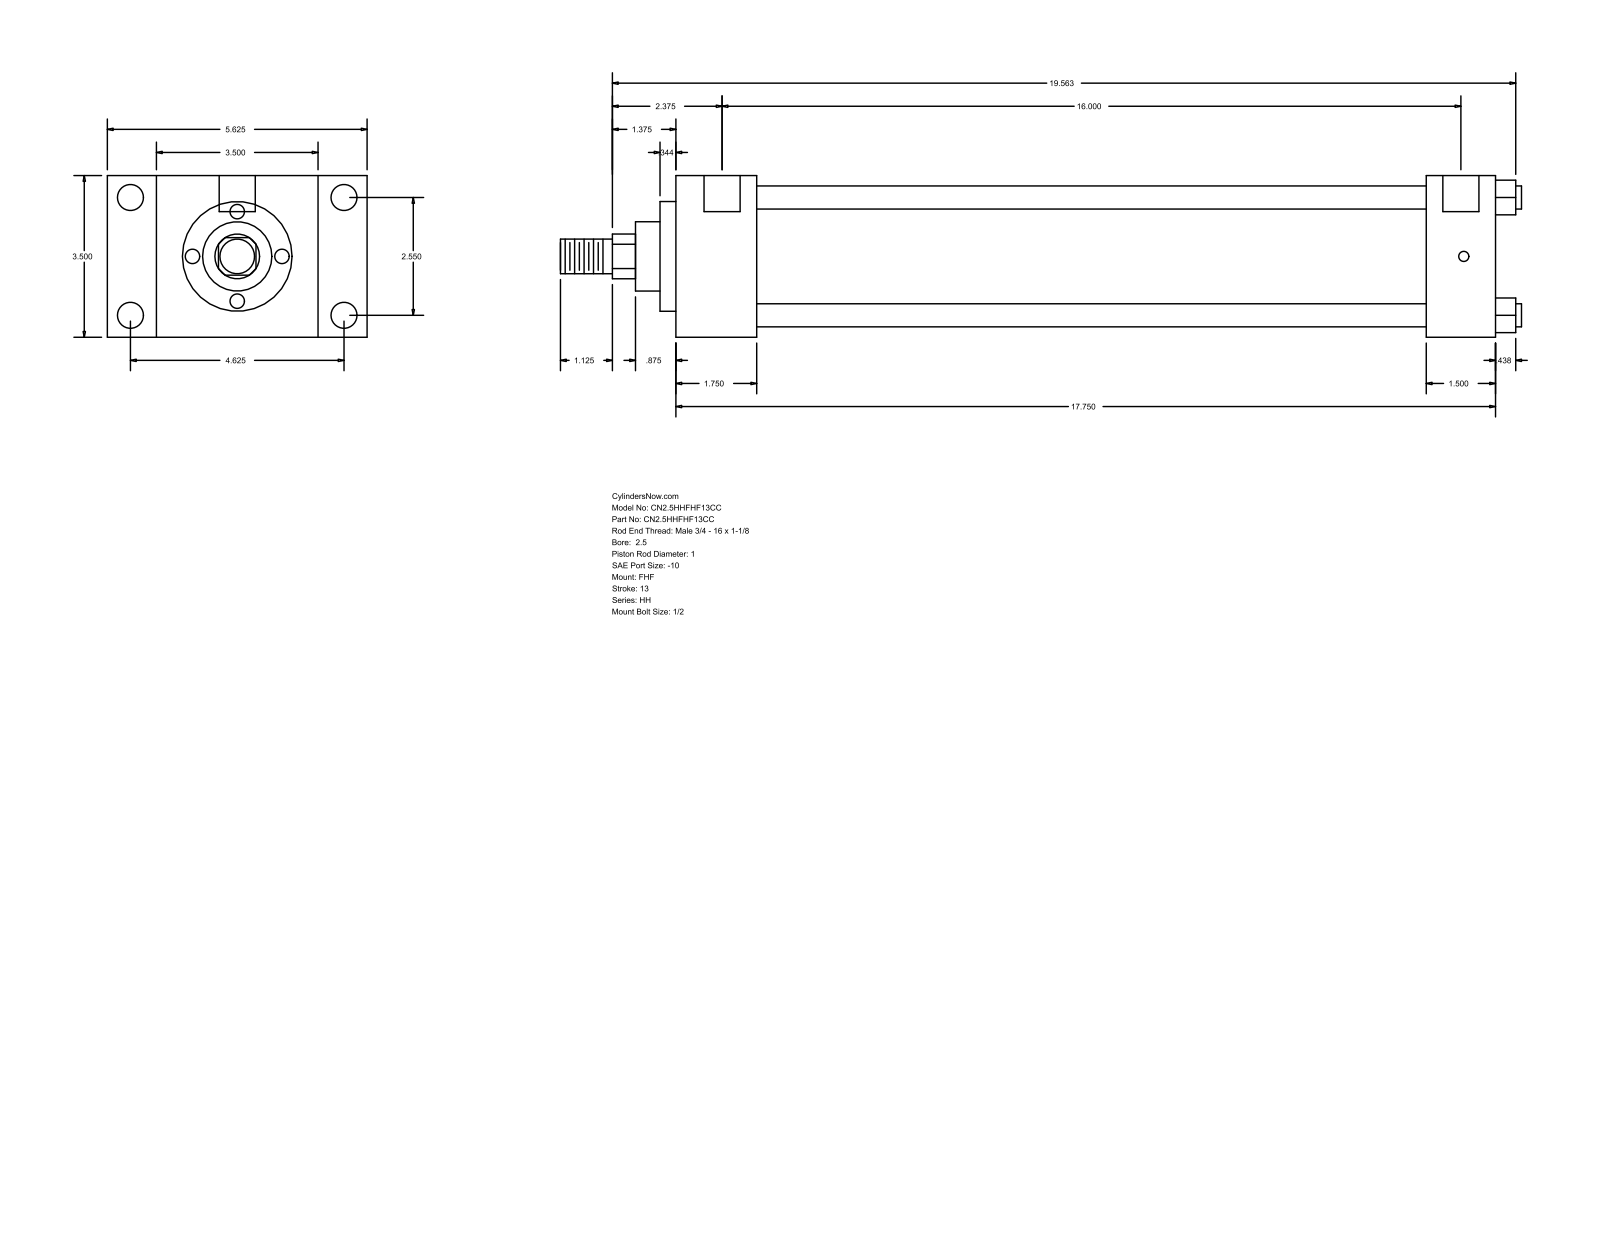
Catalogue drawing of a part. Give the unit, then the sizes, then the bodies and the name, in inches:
Units: inches
Overall size (bounding box): 20.813 × 5.625 × 3.5
Round holes (diameter × count): ⌀0.219 ×4, ⌀0.563 ×4, ⌀0.781 ×2
Round bosses / shafts (diameter × count): ⌀0.5 ×4, ⌀2.875 ×1, ⌀2.375 ×1, ⌀1.5 ×1, ⌀1 ×1, ⌀0.75 ×1
Partial cylindrical surfaces — rounded edges, fillets, slot ends (radius × count): R0.484 ×1
Main face-to-face distances: 3.5, 1.75, 1.063, 4.563, 17.75, 16, 5.625, 16.25, 14.5, 1.5
Hole centre spacings: 2.55, 4.625, 5.281, 16.125, 0.062, 0.063, 16, 16.062
Bodies: 0 solids, 90 faces (61 planar, 29 cylindrical, 0 other)
Part name (STEP PRODUCT): HH_FHF__0250_1
STEP written by: GSSL Pune (CONFIG_CONTROL_DESIGN)
